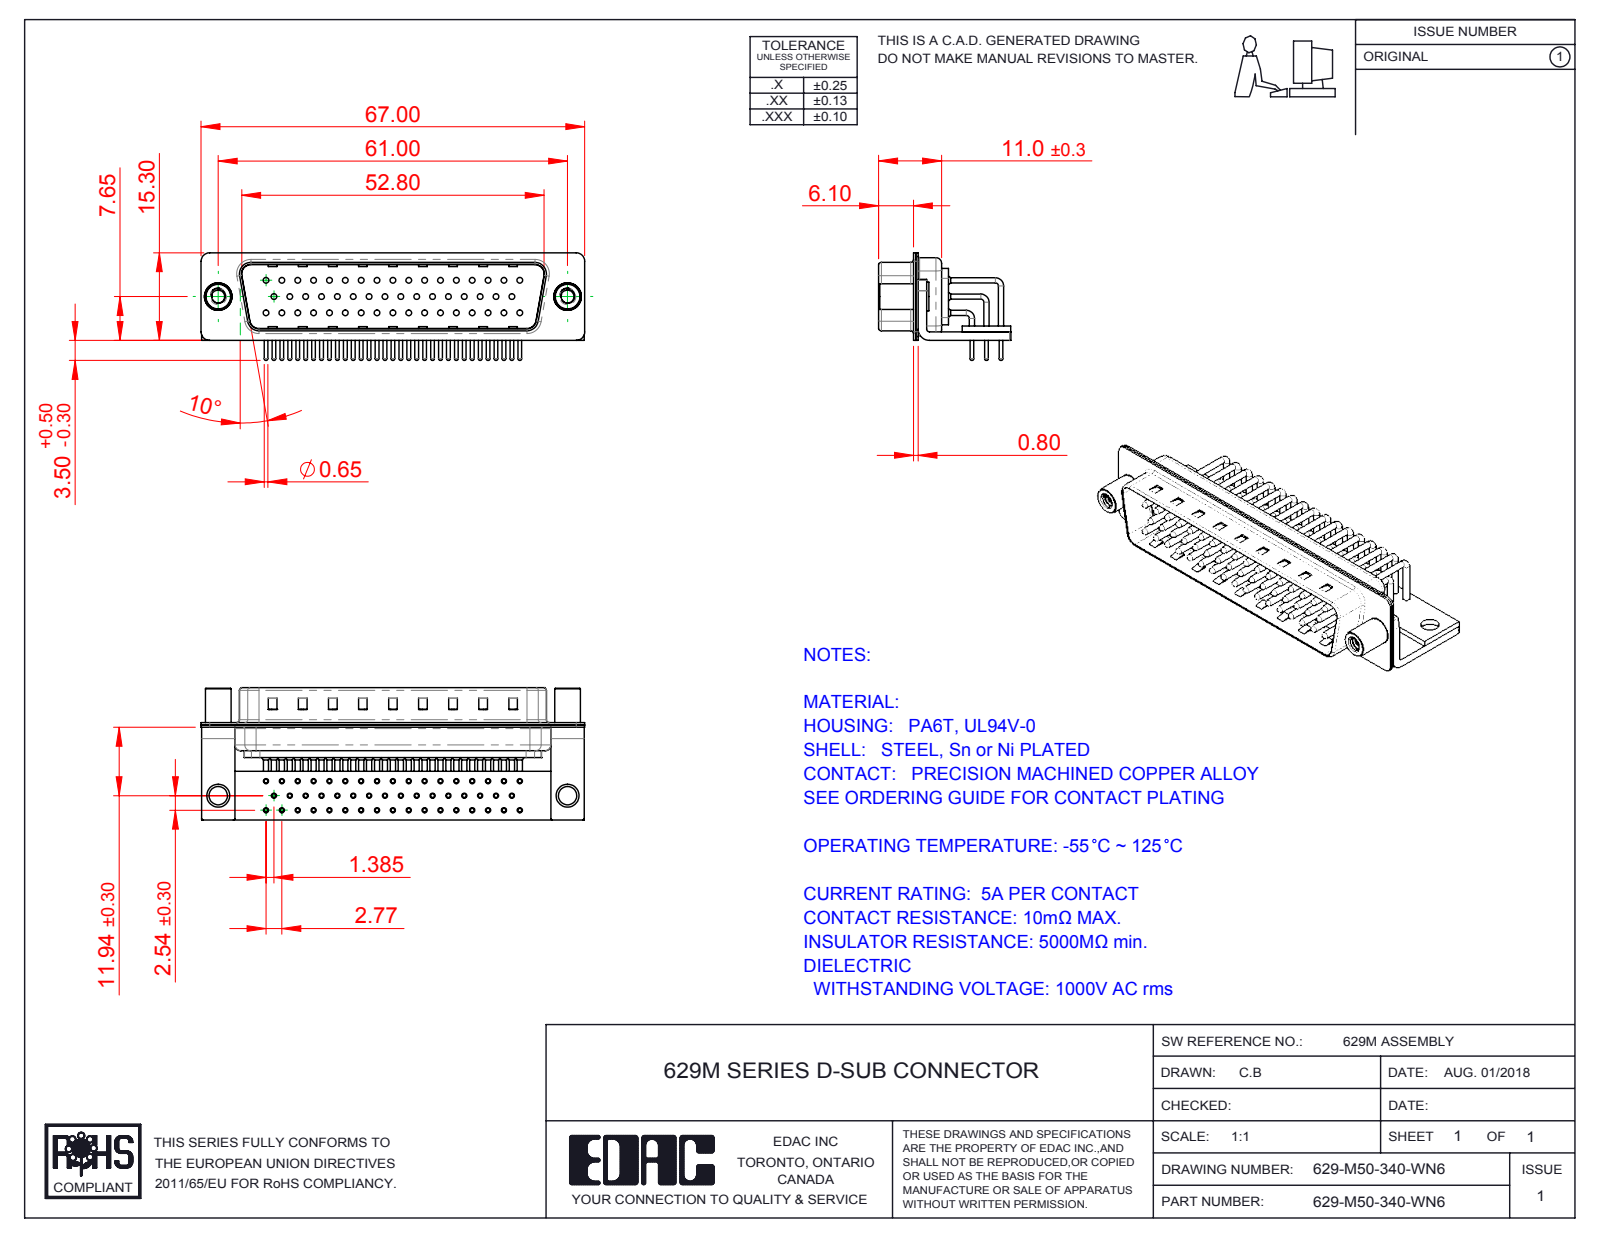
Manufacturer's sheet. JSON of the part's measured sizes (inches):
{"part_name": "629M Stabilizer Board_50 Contacts; 629M 4-40 Threaded Standoff; 629M Stabilizer Bracket_50 Contacts; 629M Contact Row 3 (+6 more)", "step_written_by": "SolidWorks 2016 (CONFIG_CONTROL_DESIGN)", "units": "inches", "bodies": {"solids": 58, "faces": 6112, "planar": 3431, "cylindrical": 2105, "other": 576}, "overall_size": [2.638, 0.909, 0.74], "volume_in3": 0.364, "surface_area_in2": 23.64, "round_holes": [[0.035, 50], [0.039, 50], [0.067, 50], [0.079, 50], [0.089, 2], [0.126, 2], [0.157, 2], [0.189, 2]], "round_bosses_or_shafts": [[0.035, 58], [0.059, 50], [0.026, 50], [0.197, 2], [0.193, 2], [0.177, 2]], "partial_cylinders_radius": [[0.04, 50], [0.01, 16], [0.059, 16], [0.079, 13], [0.02, 9], [0.063, 8], [0.024, 4], [0.026, 4]], "face_to_face_distances": [0.016, 0.039, 0.455, 0.059, 0.033, 0.224, 0.017, 0.47, 0.075, 0.031], "hole_center_spacings": [0.109, 0.218, 0.327, 0.436, 0.545, 0.654, 0.124, 0.763]}
